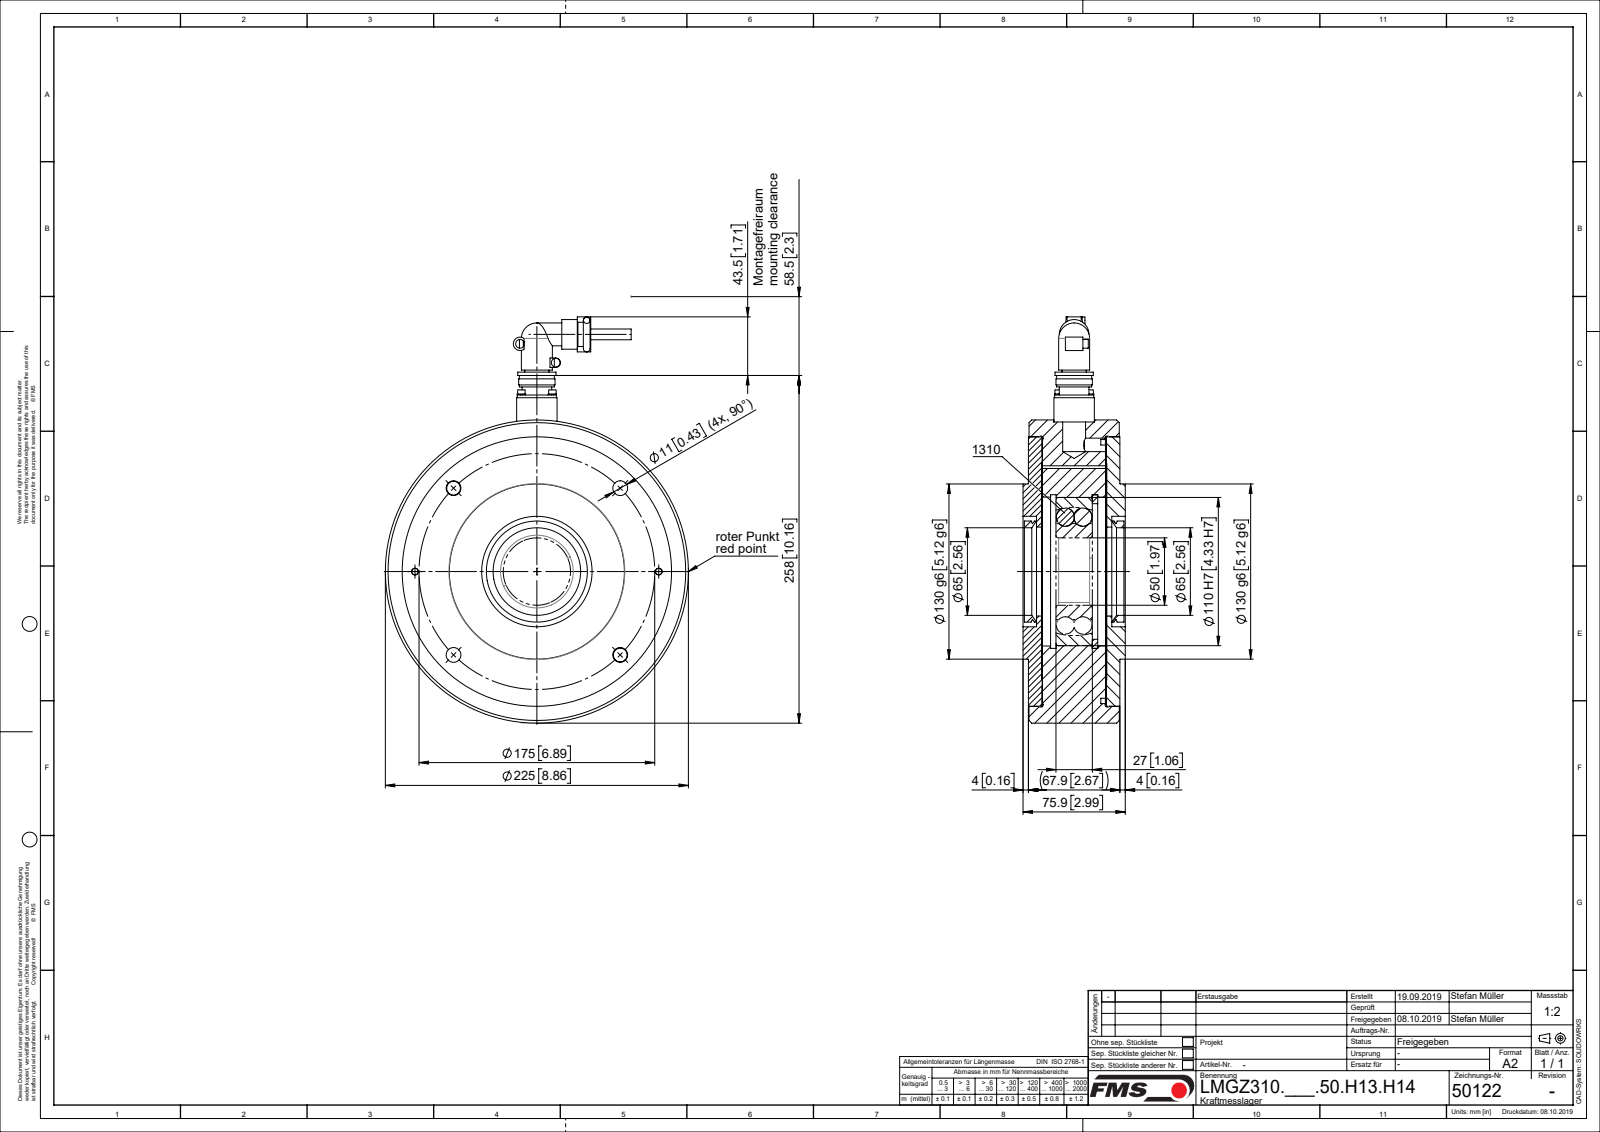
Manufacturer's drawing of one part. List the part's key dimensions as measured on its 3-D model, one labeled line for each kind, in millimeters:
Part name (STEP PRODUCT): ZEICHNUNG7; L50122; L4765504; TEIL1 (+8 more)
STEP written by: Mechanical Desktop 2007 (CONFIG_CONTROL_DESIGN)
Units: millimetres
Bodies: 21 solids, 424 faces (123 planar, 238 cylindrical, 63 other)
Overall size (bounding box): 301.5 × 225 × 75.9
Volume: 2 423 000 mm³ · Surface area: 393 594 mm²
Round holes (diameter × count): ⌀11 ×6, ⌀2.6 ×4, ⌀3.2 ×4, ⌀3.4 ×4, ⌀3.5 ×4, ⌀9 ×4, ⌀5 ×2, ⌀6.6 ×2, ⌀23 ×1, ⌀50 ×1, ⌀64 ×1, ⌀66 ×1
Round bosses / shafts (diameter × count): ⌀6.2 ×4, ⌀5.5 ×4, ⌀3 ×4, ⌀22 ×2, ⌀10 ×2, ⌀6.5 ×2, ⌀6 ×2, ⌀4.8 ×2
Partial cylindrical surfaces — rounded edges, fillets, slot ends (radius × count): R2.5 ×2, R3.5 ×1, R5 ×1, R81 ×1, R86 ×1
Main face-to-face distances: 9.7, 47.25, 10.45, 10.75, 47.45, 10.2, 57.45, 57.7, 10, 47
Hole centre spacings: 16.26, 23, 68.17, 87.5, 123.74, 164.45, 32.53, 90.5
